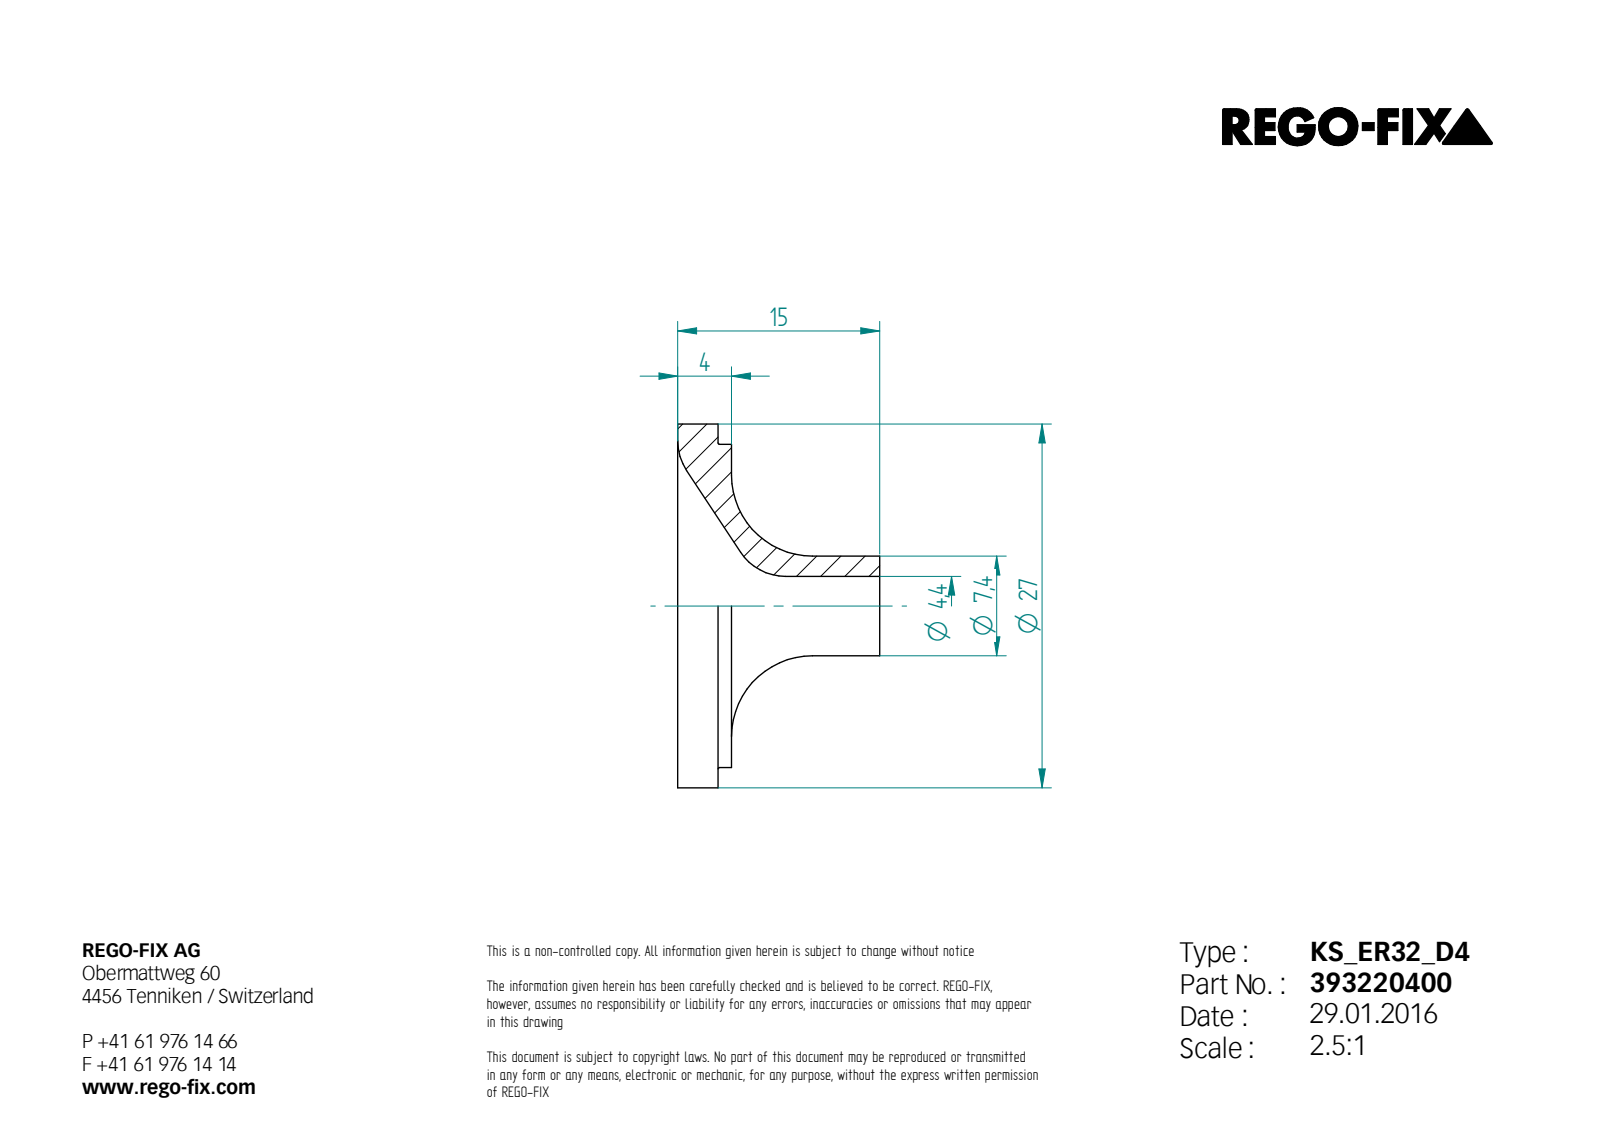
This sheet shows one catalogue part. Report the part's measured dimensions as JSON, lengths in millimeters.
{"step_written_by": "Unknown (AUTOMOTIVE_DESIGN)", "units": "millimeters", "bodies": {"solids": 1, "faces": 13, "planar": 4, "cylindrical": 4, "other": 5}, "overall_size": [27, 27, 15], "volume_mm3": 1802, "surface_area_mm2": 1847, "round_holes": [[4.4, 1]], "round_bosses_or_shafts": [[27, 1], [24, 1], [7.4, 1]], "face_to_face_distances": [1, 3, 4, 15, 12, 11]}
